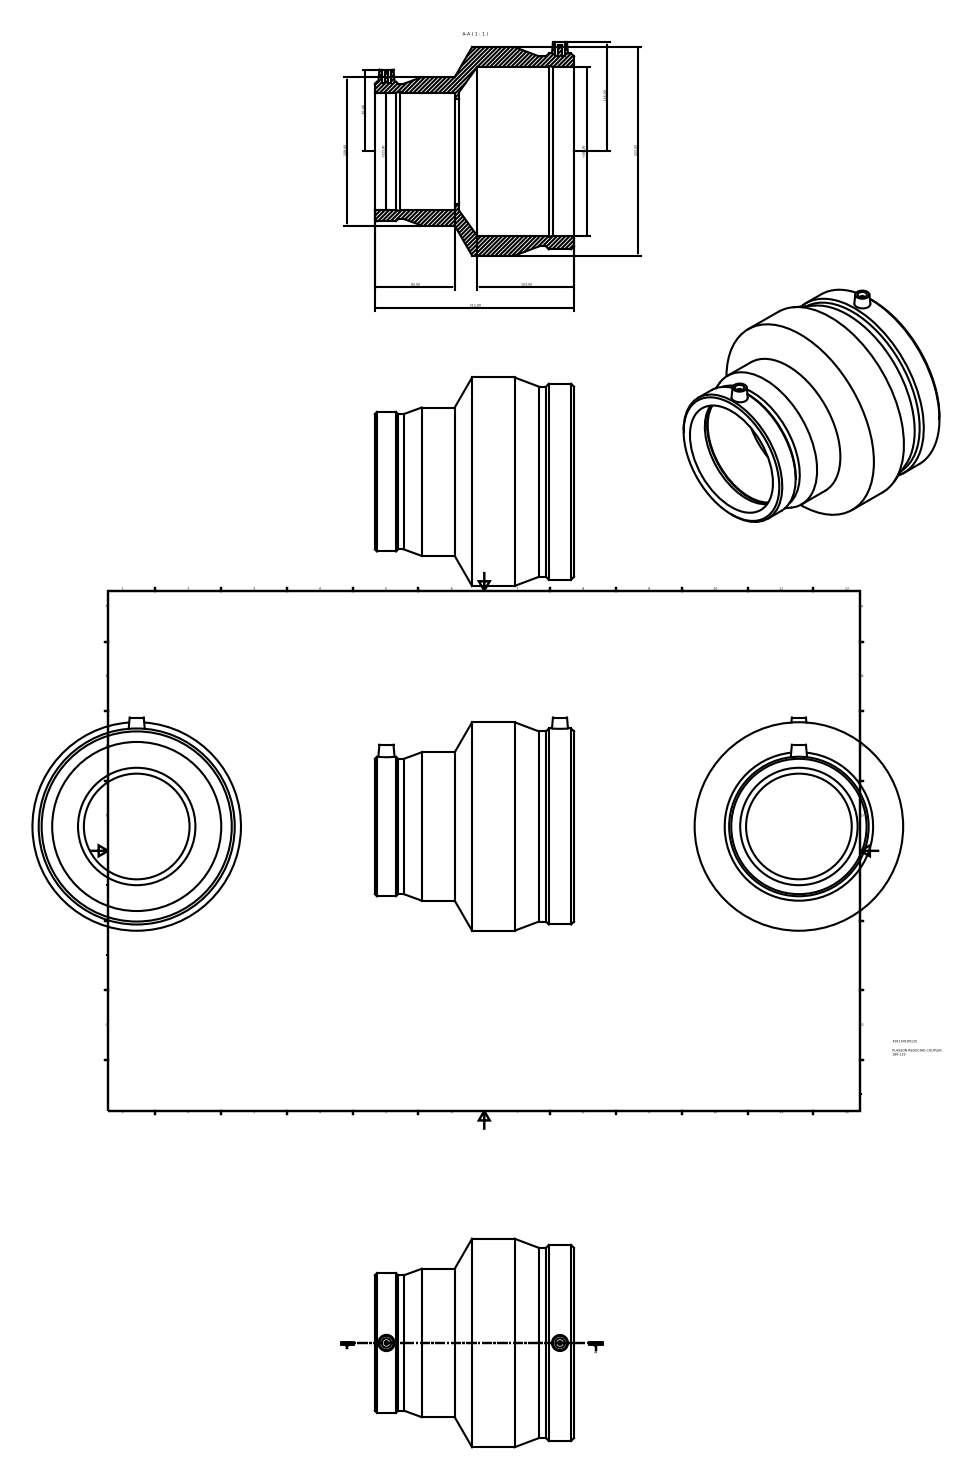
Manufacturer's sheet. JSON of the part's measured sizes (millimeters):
{"part_name": "491104180125", "step_written_by": "Autodesk Inventor 2015 (AUTOMOTIVE_DESIGN)", "units": "millimeters", "bodies": {"solids": 1, "faces": 39, "planar": 12, "cylindrical": 15, "other": 12}, "overall_size": [227, 222, 212], "volume_mm3": 1940000, "surface_area_mm2": 268274, "round_holes": [[10, 2], [112.5, 1], [125, 1], [180, 1]], "round_bosses_or_shafts": [[4, 2], [222, 1], [208.68, 1], [202.42, 1], [158, 1], [148.52, 1], [144.06, 1]], "face_to_face_distances": [212, 89.25, 122.75, 85, 4.25, 127, 185.26, 100.26, 96.01, 26.74], "hole_center_spacings": [184.73]}
